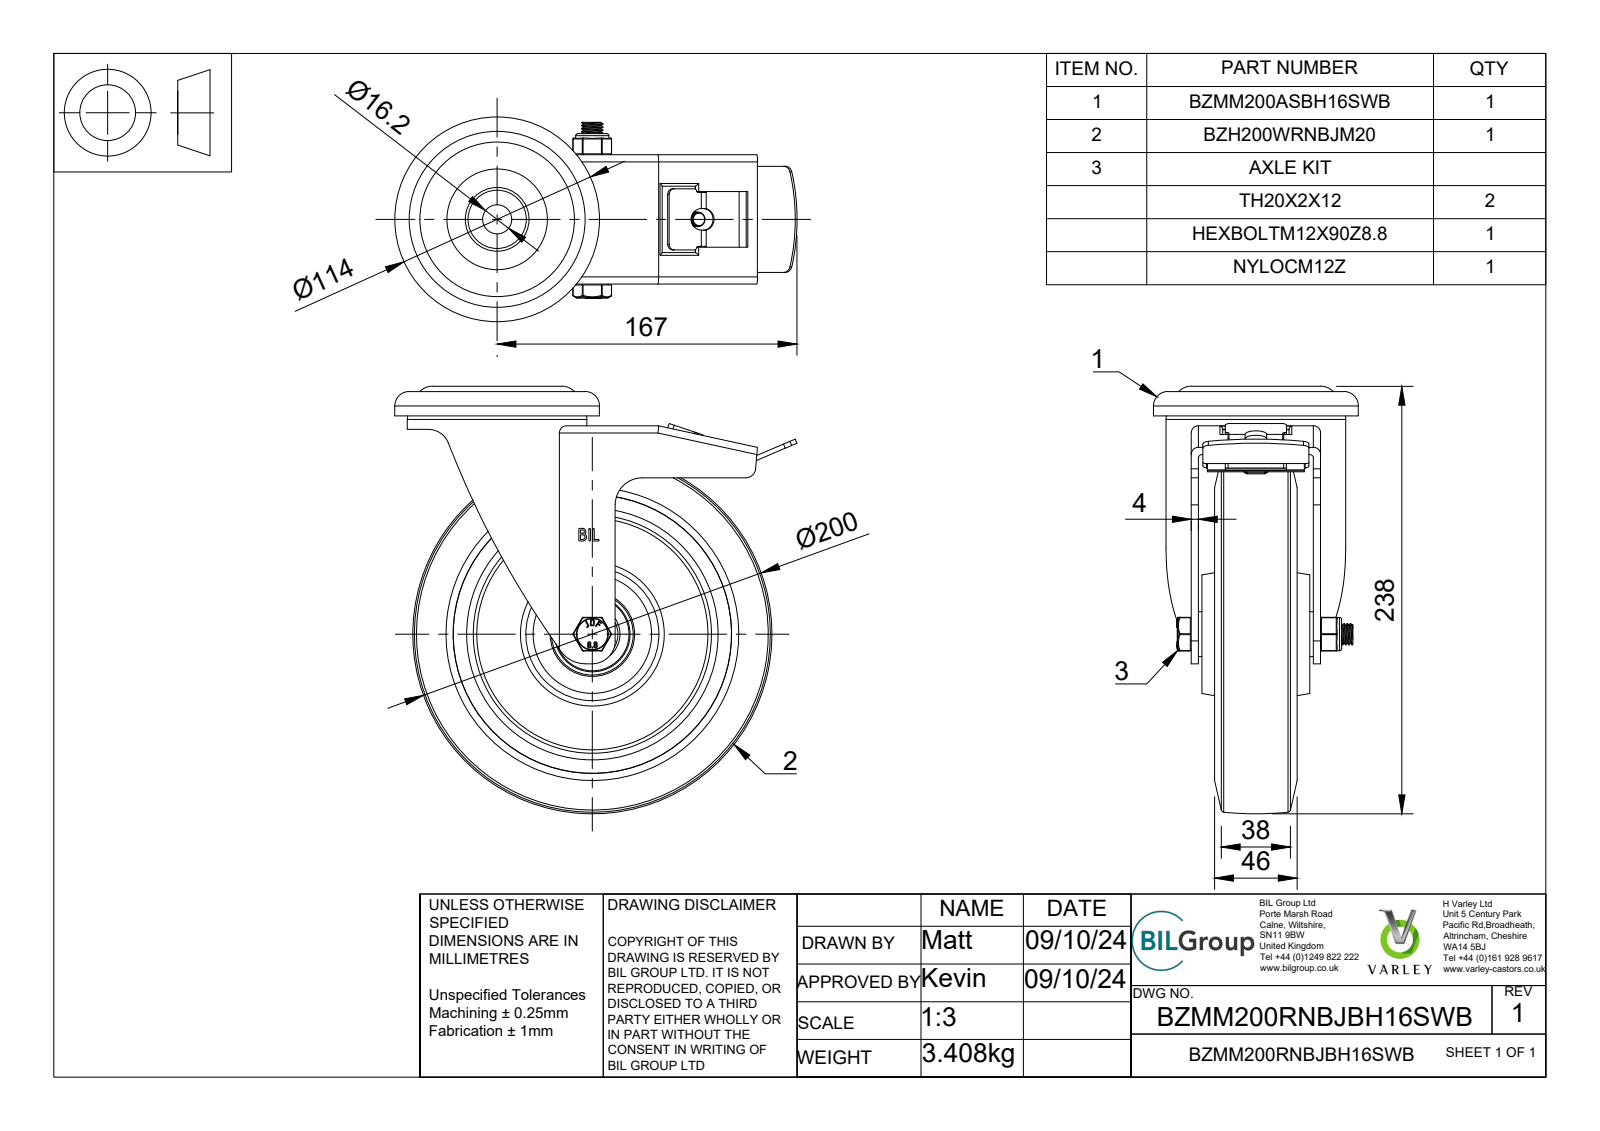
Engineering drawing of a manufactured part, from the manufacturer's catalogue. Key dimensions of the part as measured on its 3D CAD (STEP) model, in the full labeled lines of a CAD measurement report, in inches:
Part name (STEP PRODUCT): BZMM200RNBJBH16SWB v3; BZMM200ASBH16SWB - 64 v1; ZINC PLATED, PRESSED STEEL HEAD; ZINC PLATED, PRESSED STEEL FORKS (+8 more)
STEP written by: Autodesk Translation Framework v13.20.0.188 (AUTOMOTIVE_DESIGN)
Units: inches
Bodies: 39 solids, 1293 faces (554 planar, 285 cylindrical, 454 other)
Overall size (bounding box): 9.37 × 8.819 × 4.488
Volume: 76.1 in³ · Surface area: 532.2 in²
Round holes (diameter × count): ⌀0.315 ×1, ⌀0.472 ×1, ⌀0.48 ×1, ⌀0.551 ×1, ⌀0.638 ×1, ⌀0.787 ×1, ⌀1.122 ×1, ⌀1.213 ×1, ⌀1.587 ×1, ⌀1.594 ×1, ⌀1.614 ×1, ⌀1.654 ×1
Round bosses / shafts (diameter × count): ⌀4.488 ×1, ⌀3.937 ×1, ⌀2.913 ×1, ⌀1.85 ×1, ⌀1.606 ×1, ⌀1.28 ×1, ⌀1.232 ×1, ⌀1.063 ×1
Partial cylindrical surfaces — rounded edges, fillets, slot ends (radius × count): R0.039 ×25, R0.02 ×24, R0.079 ×12, R0.157 ×7, R0.059 ×6, R0.019 ×4, R0.035 ×4, R0.035 ×2
Main face-to-face distances: 0.157, 0.748, 0.512, 1.26, 2.323, 1.102, 1.417, 1.575, 0.354, 1.063
